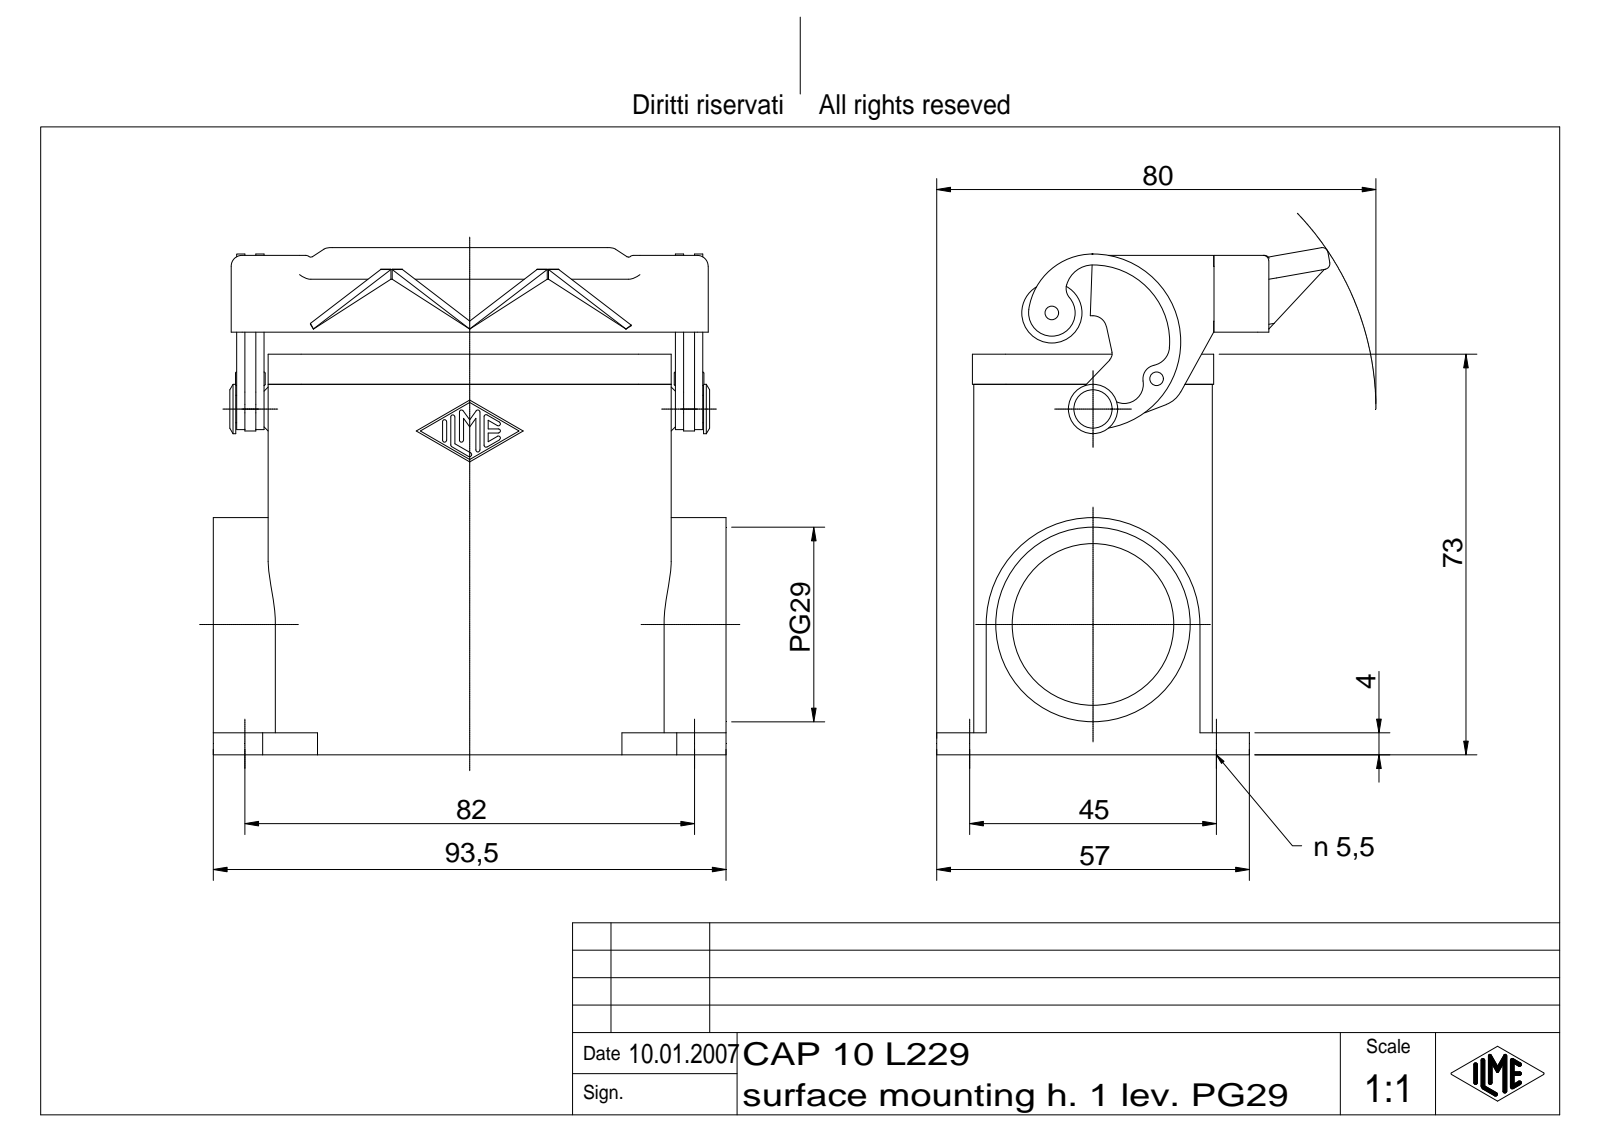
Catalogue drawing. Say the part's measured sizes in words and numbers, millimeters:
The part is named "CAP 10 L229". Its 3-D file was written by "Autodesk Inventor 7 (AUTOMOTIVE_DESIGN)". It is 4 solids with 434 faces: 164 planar, 125 cylindrical and 145 other. Overall it measures 93.5 by 92.42 by 71.7 millimeters. Its volume is 97 630 cubic millimeters and its surface area 53 747 square millimeters. Round holes: 4 of diameter 5.5, 1 of diameter 2, 1 of diameter 29.48, 1 of diameter 35.48. Round bosses or shafts: 1 of diameter 11, 1 of diameter 9, 1 of diameter 5, 1 of diameter 3, 1 of diameter 2.5. Partial cylindrical surfaces (rounded edges, fillets, slot ends): 14 of radius 0.38, 12 of radius 2, 8 of radius 6, 7 of radius 1, 5 of radius 1.5, 4 of radius 3, 3 of radius 2.5, 2 of radius 3.5. The main face-to-face distances are 3, 40.5, 4, 43.5, 37.5, 67.5, 8.75, 11.75, 61.75, 70.5. The hole center spacings are 45, 82, 93.54, 46.24.
